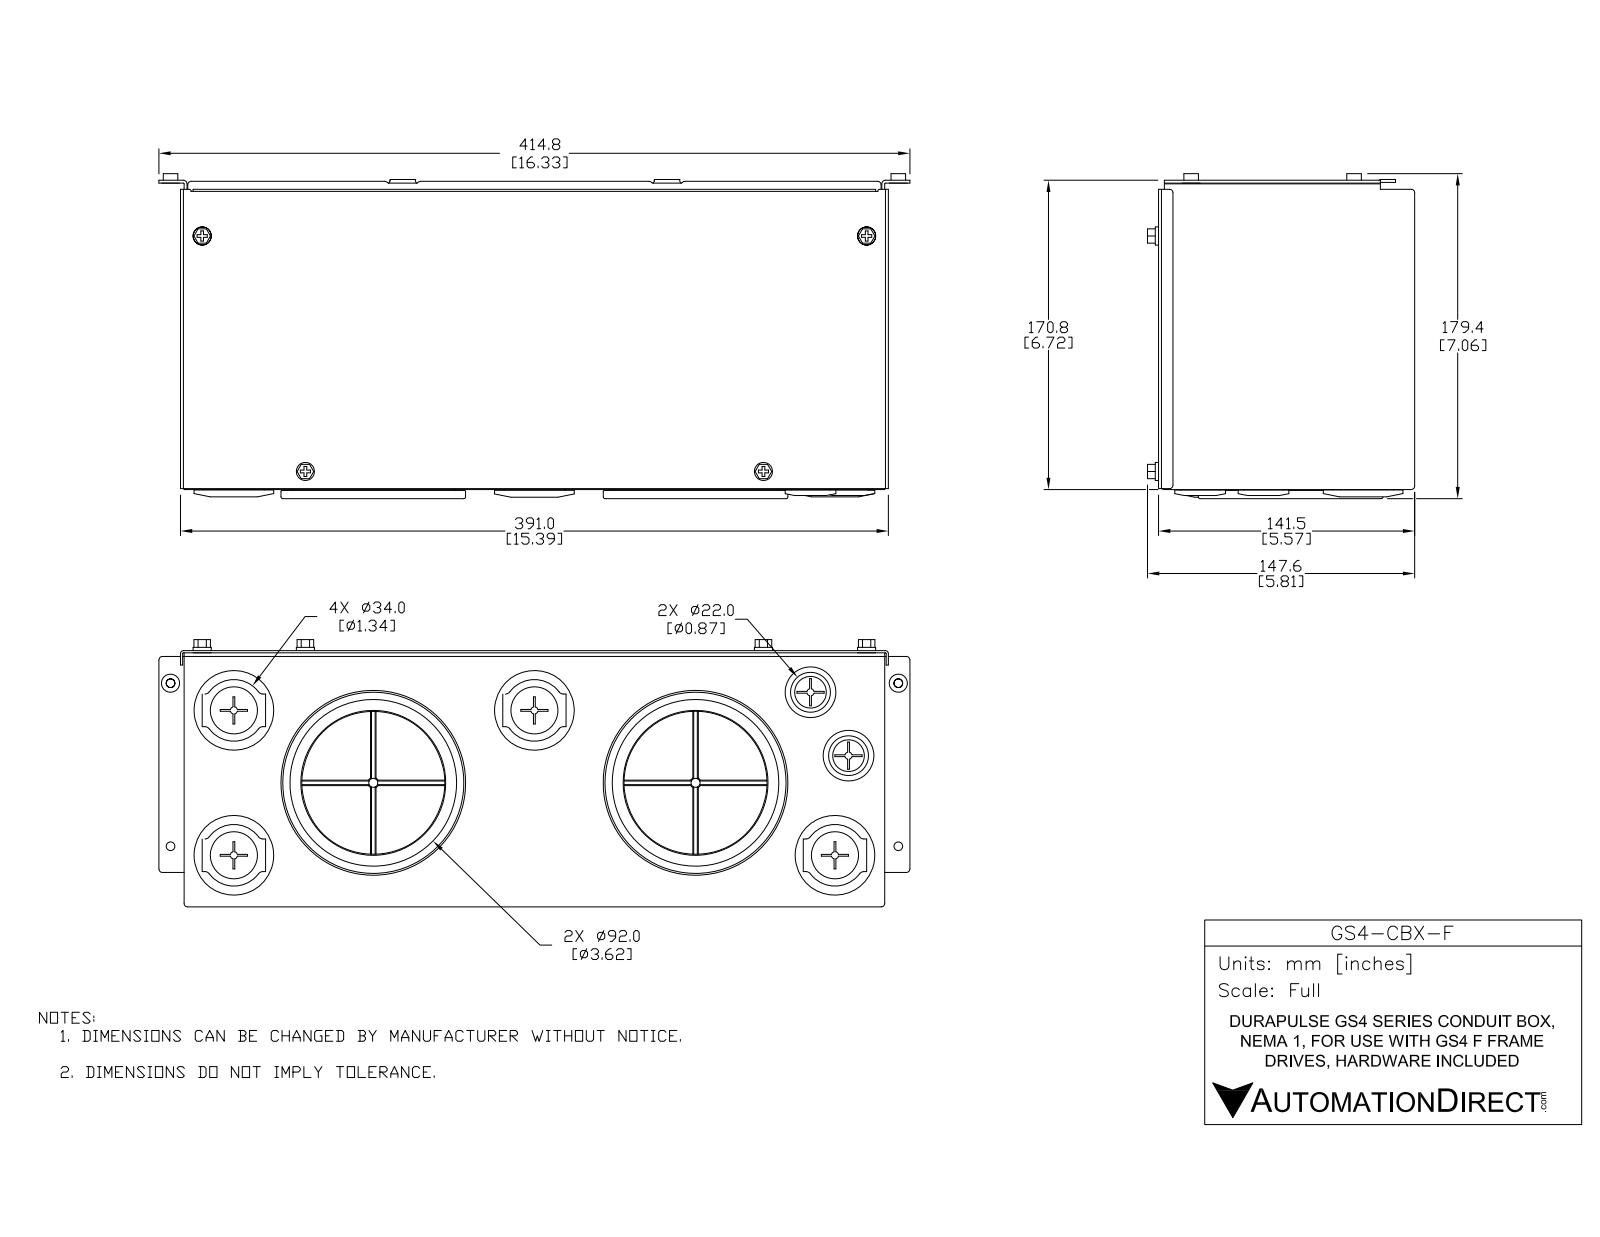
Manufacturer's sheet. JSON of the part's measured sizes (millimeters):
{"part_name": "GS4-CBX-F; 3105162300-SCREW-M5 A; 32450037XX_RUBBER_3INCH_2 A; 3240061300_RUBBER22_4 A (+3 more)", "step_written_by": "SolidWorks 2015 (AUTOMOTIVE_DESIGN)", "units": "millimeters", "bodies": {"solids": 18, "faces": 795, "planar": 390, "cylindrical": 302, "other": 103}, "overall_size": [414.8, 176.3, 146.9], "volume_mm3": 474400, "surface_area_mm2": 570900, "round_holes": [[4.8, 12], [4.9, 4], [6, 4], [6.5, 4], [26.5, 4], [5, 2], [16.5, 2], [22, 2], [35, 2], [80.6, 2], [83, 2], [92, 2]], "round_bosses_or_shafts": [[44, 4], [33.5, 4], [9.9, 4], [8, 4], [7.5, 4], [4.8, 4], [102, 2], [97, 2]], "partial_cylinders_radius": [[0.5, 38], [2, 28], [1, 21], [0.4, 7], [0.8, 6], [1.6, 5], [4.4, 4], [1.7, 2]], "face_to_face_distances": [1.6, 138.7, 1.2, 139.9, 140.3, 141.5, 385.4, 383.8, 387, 164.2], "hole_center_spacings": [90, 0.8, 402, 412, 86.8, 258.1, 35.4, 97.6]}
